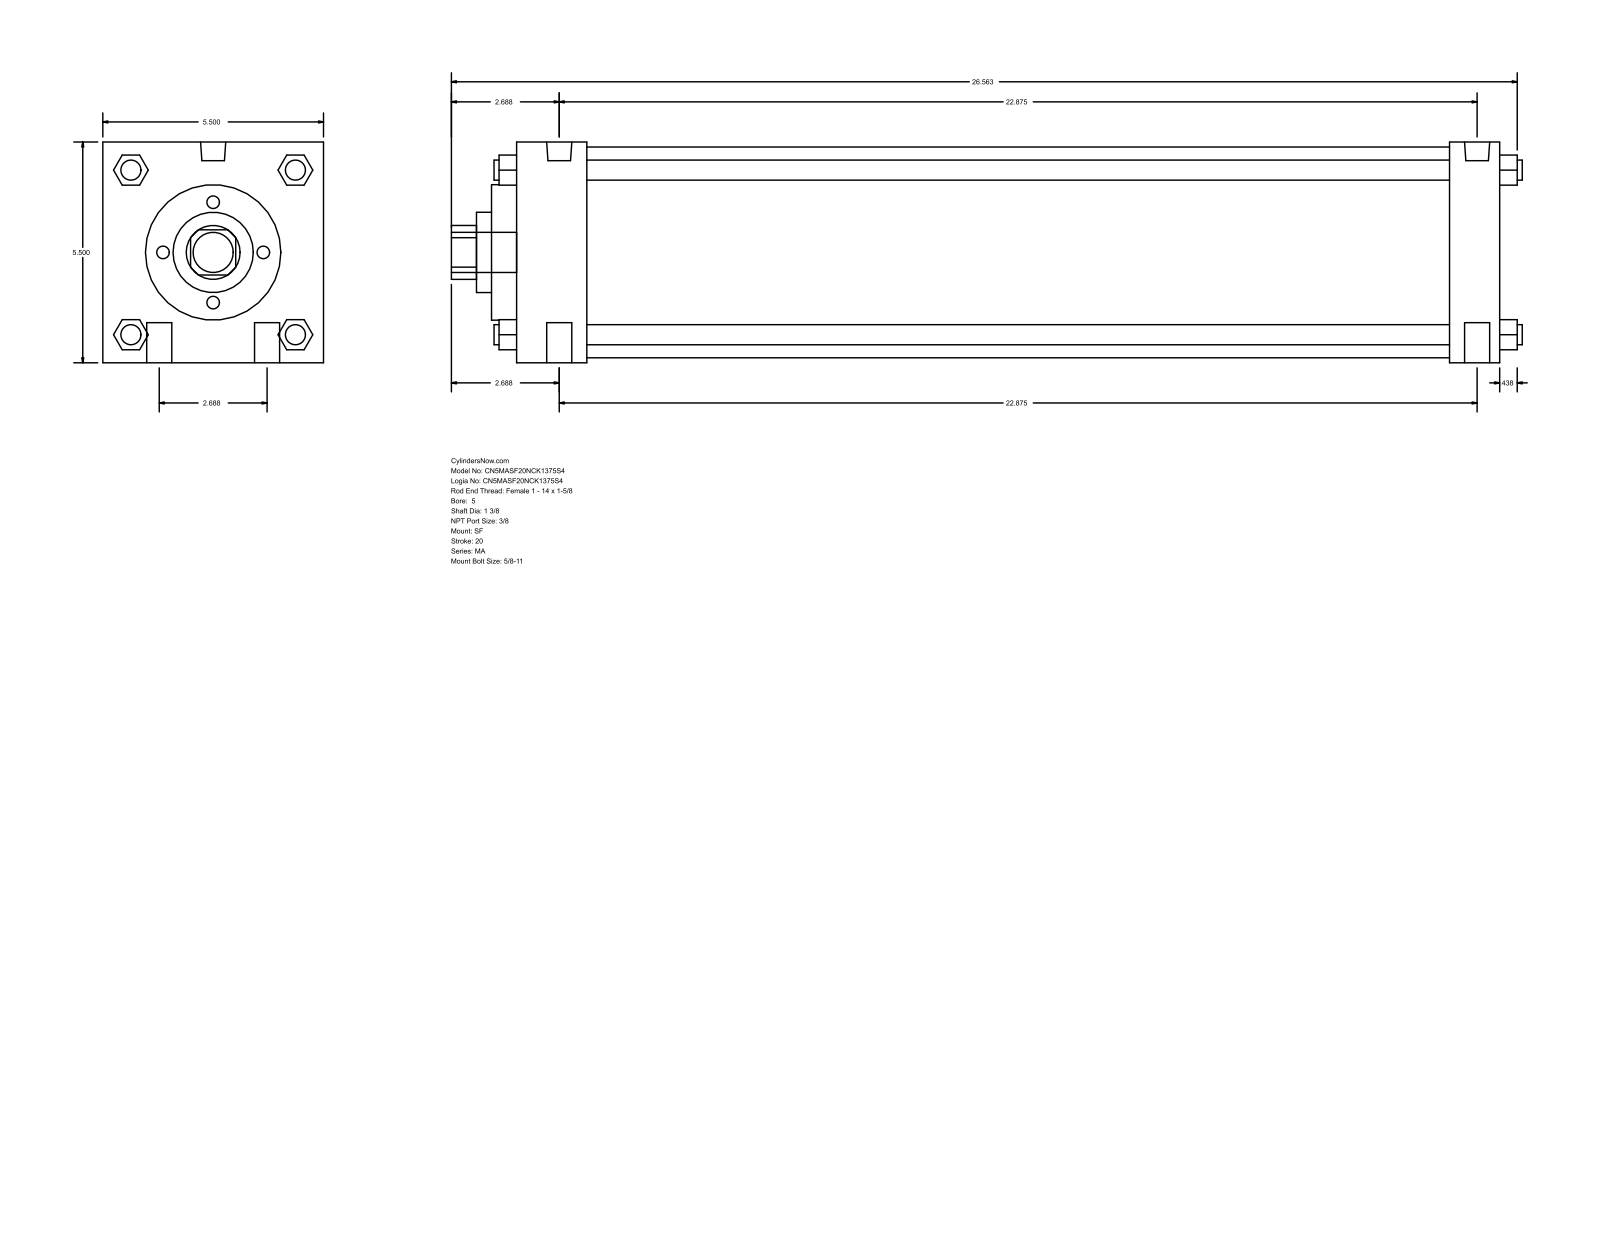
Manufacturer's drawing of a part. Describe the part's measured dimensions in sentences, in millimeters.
The part is named "MA_SF__0500_1.375". Its 3-D file was written by "GSSL Pune (CONFIG_CONTROL_DESIGN)". It is 0 solids with 126 faces: 95 planar, 31 cylindrical and 0 other. Overall it measures 677.86 by 139.7 by 139.7 millimeters. Round holes: 1 of diameter 34.92, 1 of diameter 50.8, 1 of diameter 85.72, 1 of diameter 133.35. Round bosses or shafts: 4 of diameter 15.88, 4 of diameter 12.7, 2 of diameter 15.93, 2 of diameter 11.11, 1 of diameter 25.4. Partial cylindrical surfaces (rounded edges, fillets, slot ends): 1 of radius 17.06. The main face-to-face distances are 139.7, 622.31, 44.45, 590.56, 546.11, 577.86, 31.75, 15.87, 60.32, 606.43.
